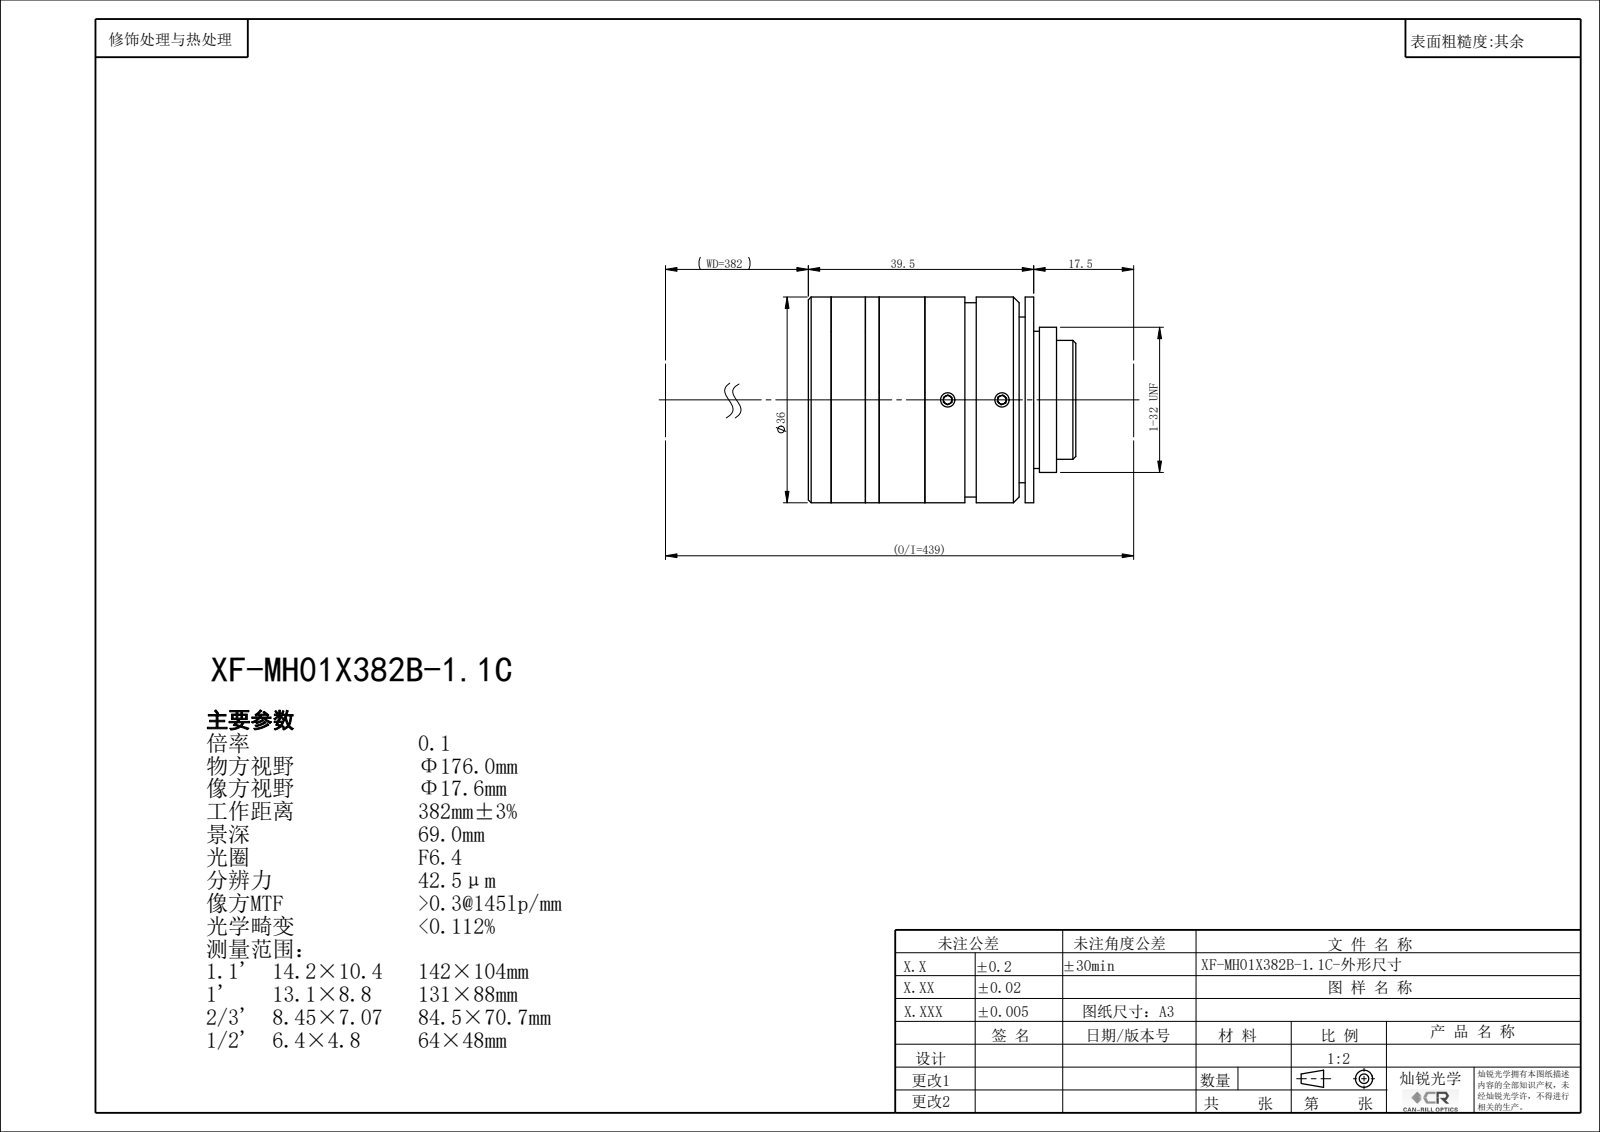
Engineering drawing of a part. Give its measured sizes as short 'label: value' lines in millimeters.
name: XF-MH01X382B-1.1C
written by: SolidWorks 2022 (CONFIG_CONTROL_DESIGN)
unit: mm
bodies: 0 solids, 152 faces (76 planar, 50 cylindrical, 26 other)
size: 46.82 × 36 × 36
holes: 6× ⌀2.5, 1× ⌀14, 1× ⌀16.4, 1× ⌀17, 1× ⌀18.4, 1× ⌀22.4, 1× ⌀24, 1× ⌀24.9, 1× ⌀26
bosses: 1× ⌀36, 1× ⌀34, 1× ⌀25.4, 1× ⌀20.8
face distances: 19.06, 39.46, 20.4, 1.5, 37.96, 17.56, 8, 25.56, 33.46, 12.4
hole spacings: 9.5
